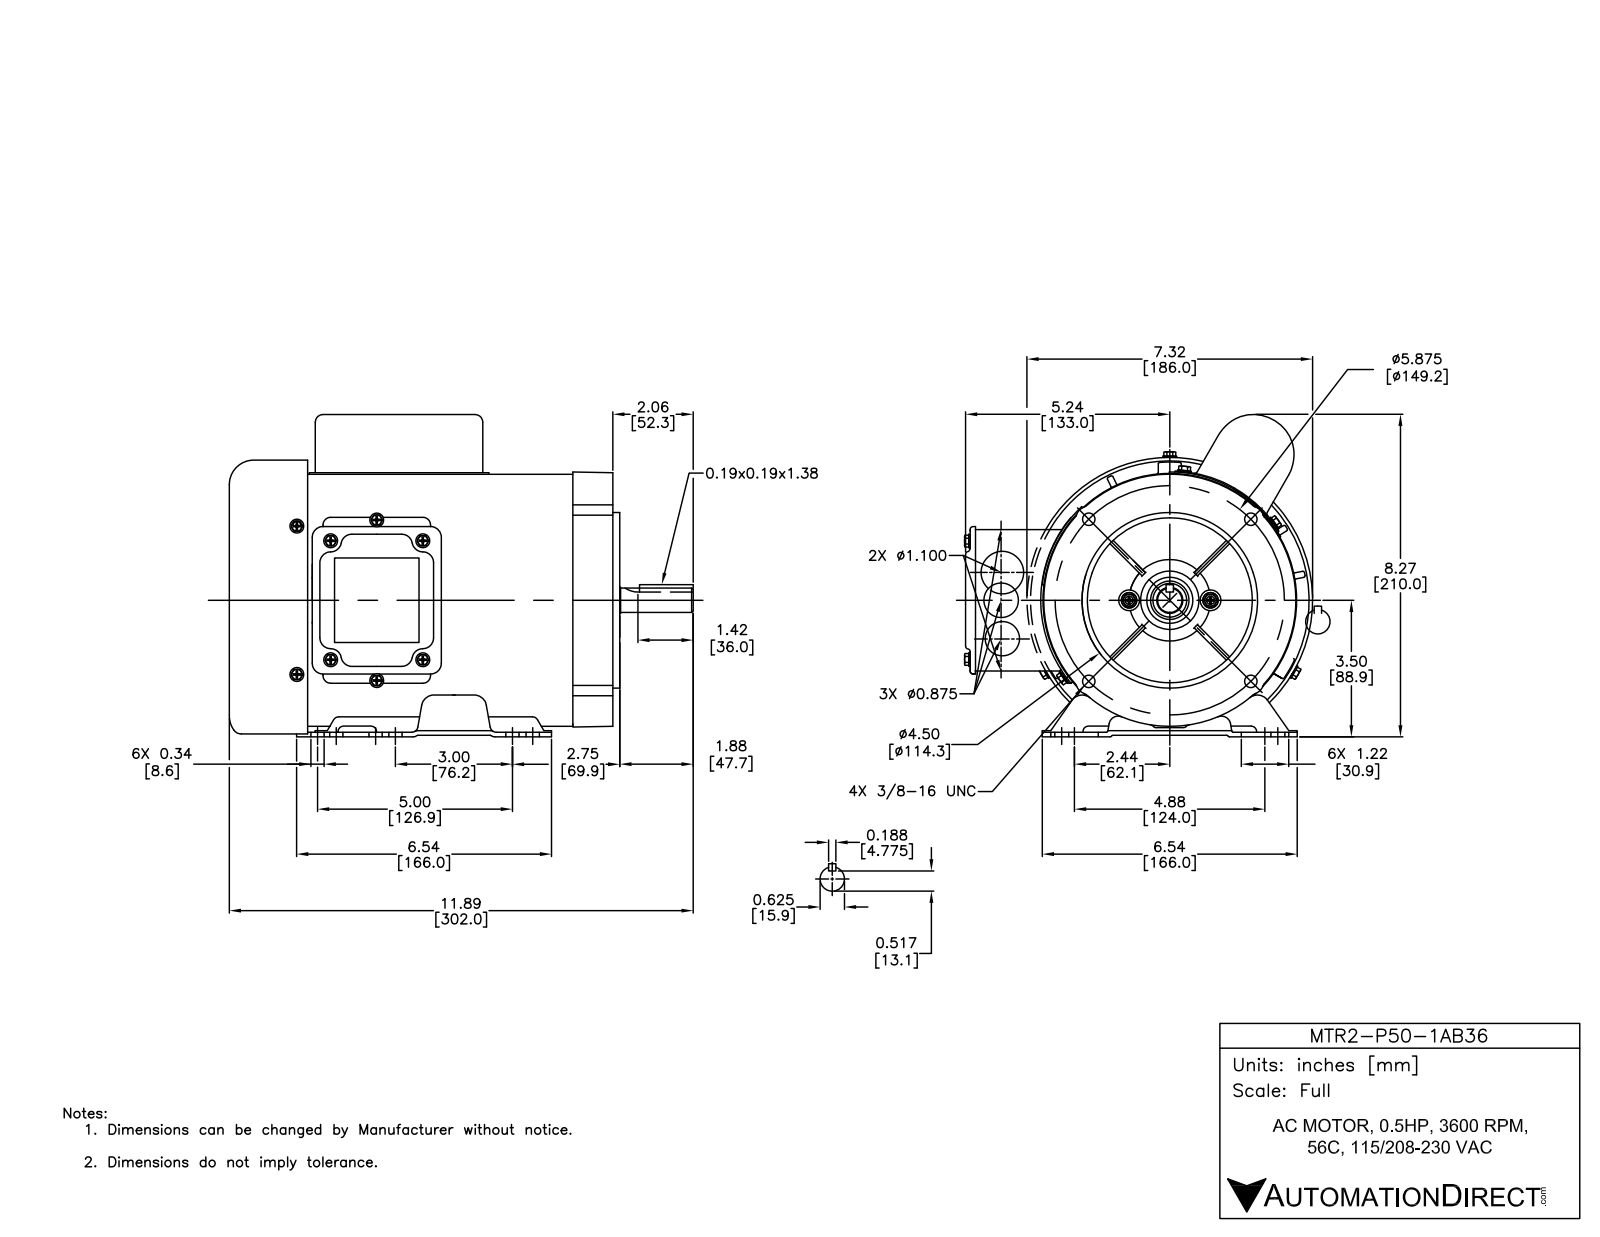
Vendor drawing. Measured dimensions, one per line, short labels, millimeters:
name: Cap cover bolt; Cap cover; Fan; Elec Cover bolt Hex Washer Screw_AI_IN-HWMS 0.164-32x0.3125x0.3125-N (+8 more)
written by: SolidWorks 2015 (AUTOMOTIVE_DESIGN)
unit: mm
bodies: 54 solids, 2456 faces (924 planar, 1005 cylindrical, 527 other)
size: 302 × 255.3 × 246.6
volume: 877 700 mm³; area: 709 000 mm²
holes: 13× ⌀5.6, 12× ⌀5, 8× ⌀7, 6× ⌀5.5, 6× ⌀6.3, 6× ⌀8.7, 5× ⌀3.5, 4× ⌀3.9, 4× ⌀8, 3× ⌀18, 2× ⌀3.3, 2× ⌀3.4
bosses: 13× ⌀8.8, 13× ⌀4.2, 4× ⌀6.3, 2× ⌀14, 2× ⌀10.5, 2× ⌀4.8, 1× ⌀182.5, 1× ⌀165
rounds: 101× R3, 66× R1, 24× R5.8, 23× R1.9, 22× R5, 17× R7, 16× R2.5, 14× R3
face distances: 1, 6, 3, 35.6, 1.6, 213, 41.6, 1.9, 34.6, 40.6
hole spacings: 77, 60, 107.2, 97.6, 2.4, 74.6, 95.2, 105.5
